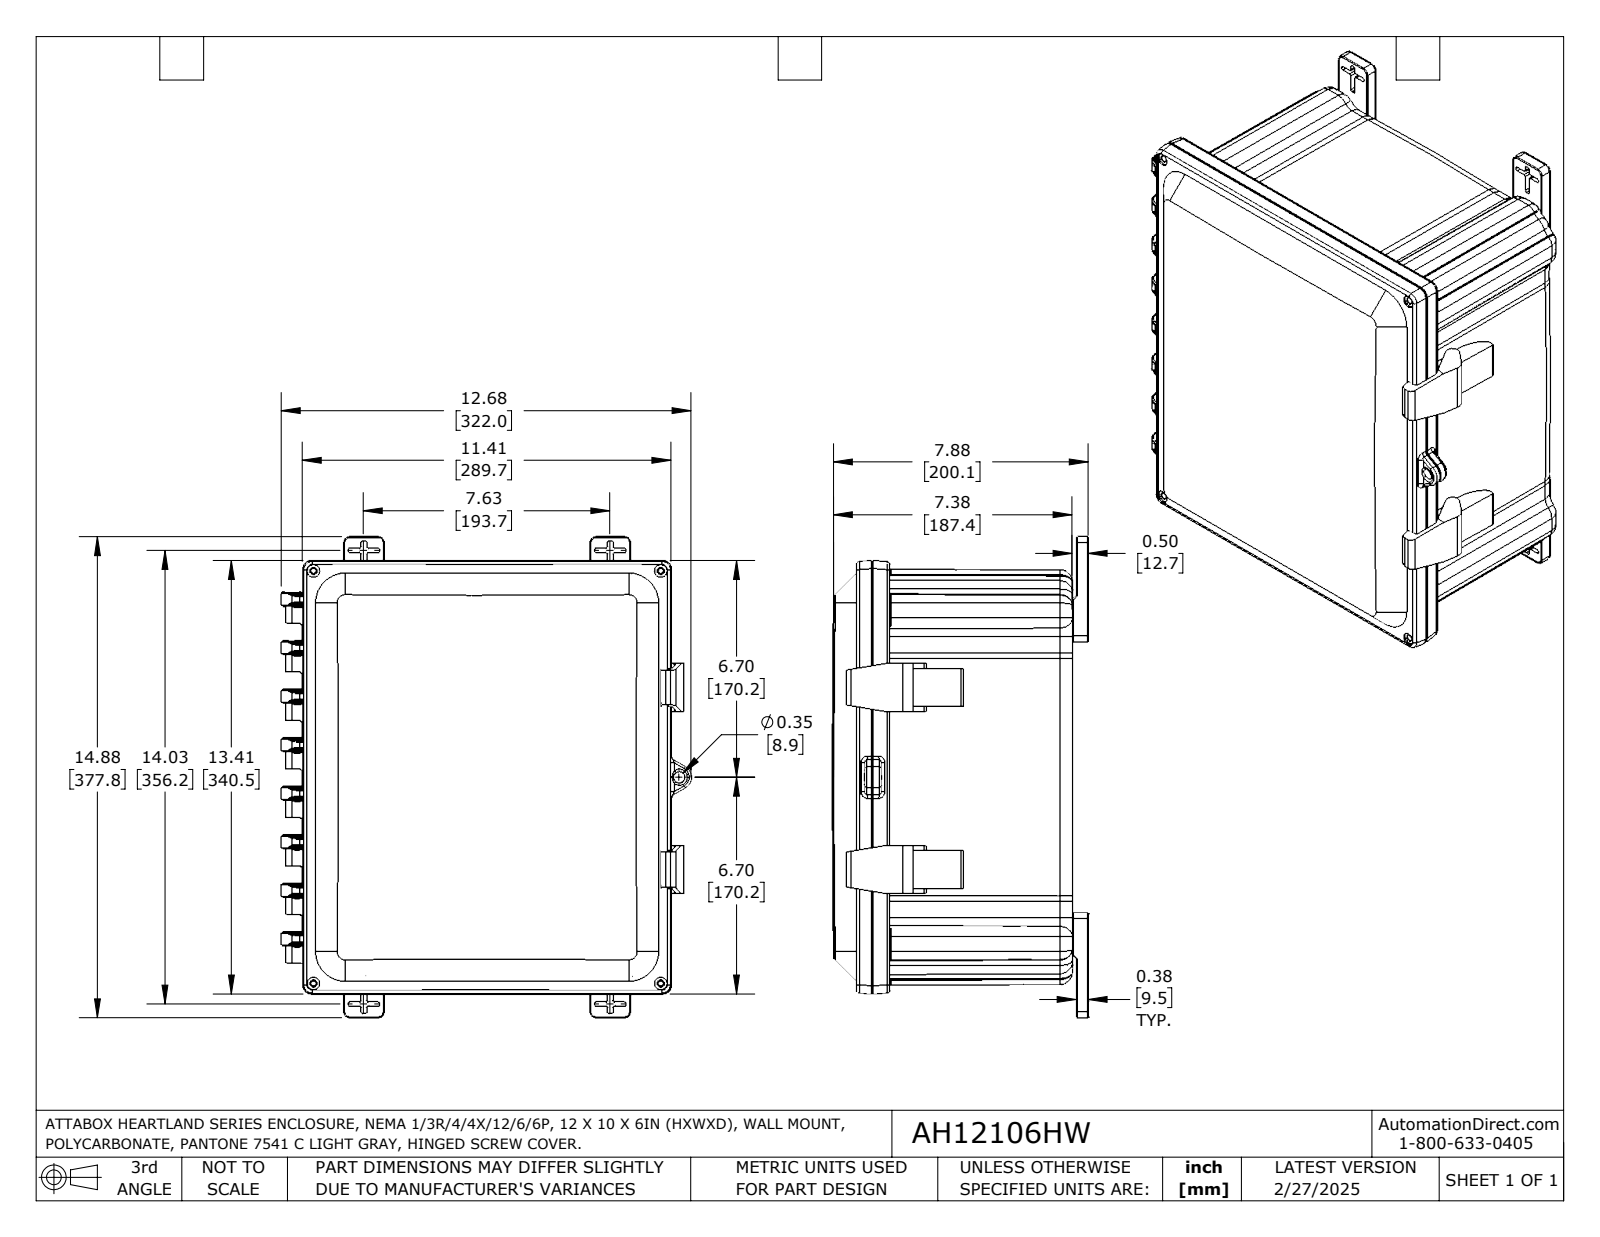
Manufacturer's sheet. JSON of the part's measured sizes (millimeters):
{"part_name": "AH12106HW", "step_written_by": "SolidWorks 2024 (AUTOMOTIVE_DESIGN)", "units": "millimeters", "bodies": {"solids": 6, "faces": 2578, "planar": 703, "cylindrical": 817, "other": 1058}, "overall_size": [377.8, 322, 200.1], "volume_mm3": 2032000, "surface_area_mm2": 890300, "round_holes": [[4, 8], [5, 4], [6.4, 4], [8, 4], [9.9, 4], [8.3, 1], [9.5, 1], [11.4, 1]], "round_bosses_or_shafts": [[6.4, 4], [8, 1]], "partial_cylinders_radius": [[0.9, 144], [1.3, 116], [1.7, 89], [0.5, 32], [0.8, 30], [0.6, 26], [0.3, 25], [4.6, 16]], "face_to_face_distances": [3.6, 156, 152.4, 12.7, 4.7, 168.7, 3.6, 7.4, 10.9, 143.3], "hole_center_spacings": [236.7, 243.4, 367.7, 273.1, 11.2, 44.9, 56.1, 201.8]}
